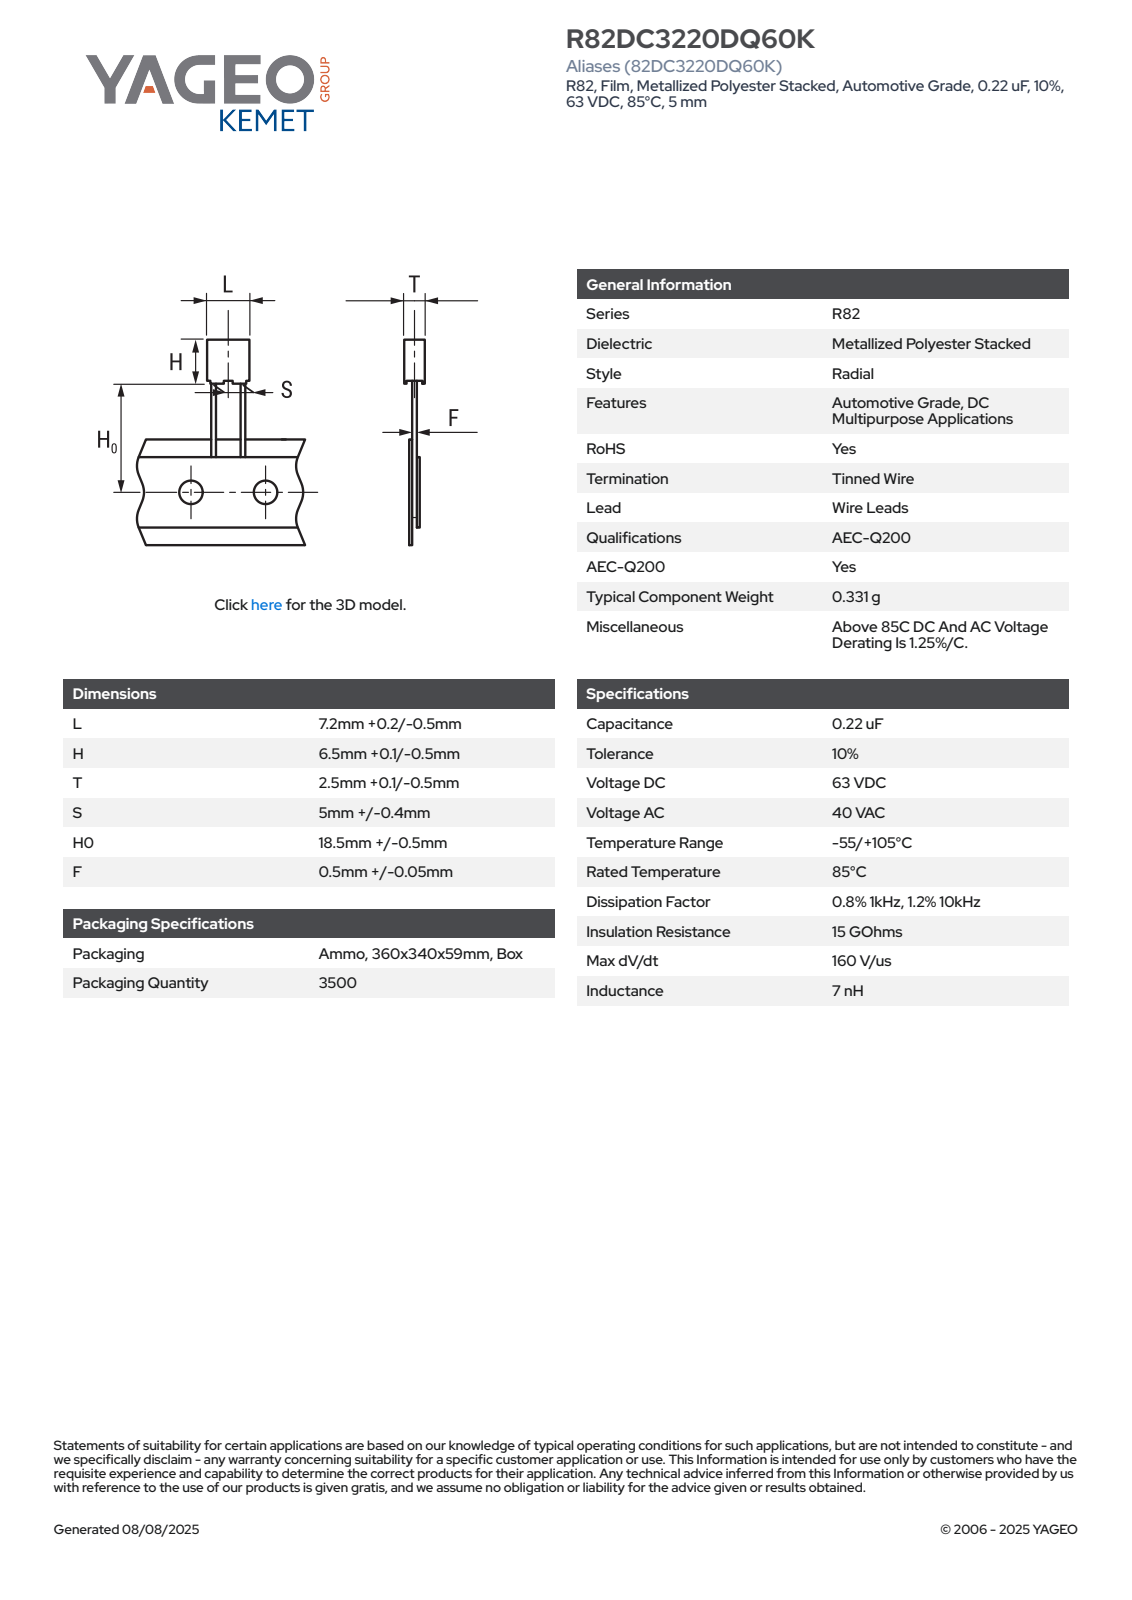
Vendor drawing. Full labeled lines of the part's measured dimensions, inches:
Part name (STEP PRODUCT): CFR_RB3_7.2X6.5X2.5_L7.4H6.6T2.6S5H019F0.55
STEP written by: SolidWorks 2021 (AUTOMOTIVE_DESIGN)
Units: inches
Bodies: 4 solids, 85 faces (77 planar, 8 cylindrical, 0 other)
Overall size (bounding box): 1.008 × 0.291 × 0.102
Volume: 0.008 in³ · Surface area: 0.388 in²
Round bosses / shafts (diameter × count): ⌀0.022 ×2
Partial cylindrical surfaces — rounded edges, fillets, slot ends (radius × count): R0.02 ×4
Main face-to-face distances: 0.102, 0.291, 0.23, 0.093, 0.083, 0.03, 0.26, 0.281, 0.272, 0.02
